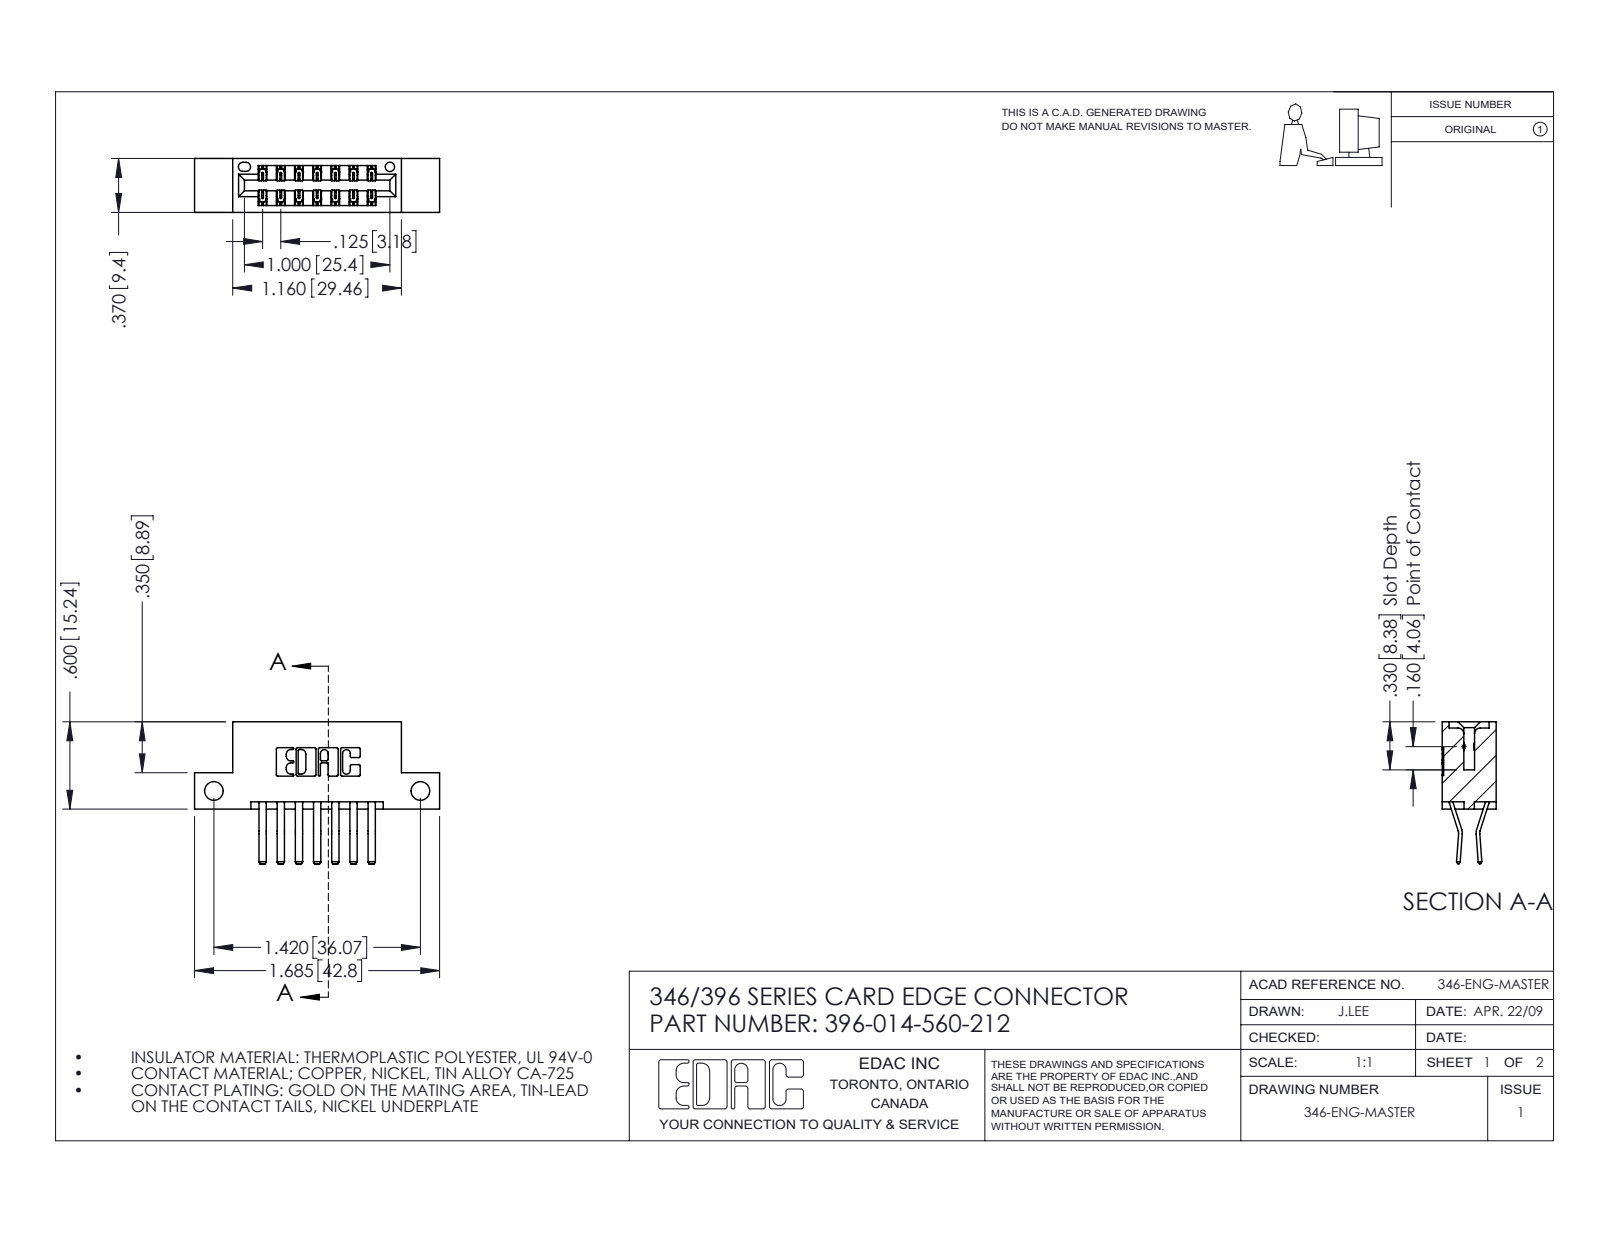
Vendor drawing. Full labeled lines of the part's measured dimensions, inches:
Part name (STEP PRODUCT): 346 Part_Flush Mounting Lugs - Side Mount; 345-292-001_560 Tail; 396-014-560-212
STEP written by: SolidWorks 2016 (CONFIG_CONTROL_DESIGN)
Units: inches
Bodies: 15 solids, 878 faces (566 planar, 312 cylindrical, 0 other)
Overall size (bounding box): 1.685 × 0.975 × 0.37
Volume: 0.238 in³ · Surface area: 7.636 in²
Round holes (diameter × count): ⌀0.128 ×2, ⌀0.064 ×1
Partial cylindrical surfaces — rounded edges, fillets, slot ends (radius × count): R0.01 ×22, R0.006 ×21, R0.007 ×6, R0.031 ×6, R0.026 ×3, R0.01 ×2, R0.014 ×2, R0.022 ×2
Main face-to-face distances: 0.25, 0.37, 0.048, 0.322, 0.025, 0.148, 0.222, 0.1, 0.174, 0.072
Hole centre spacings: 1.42
